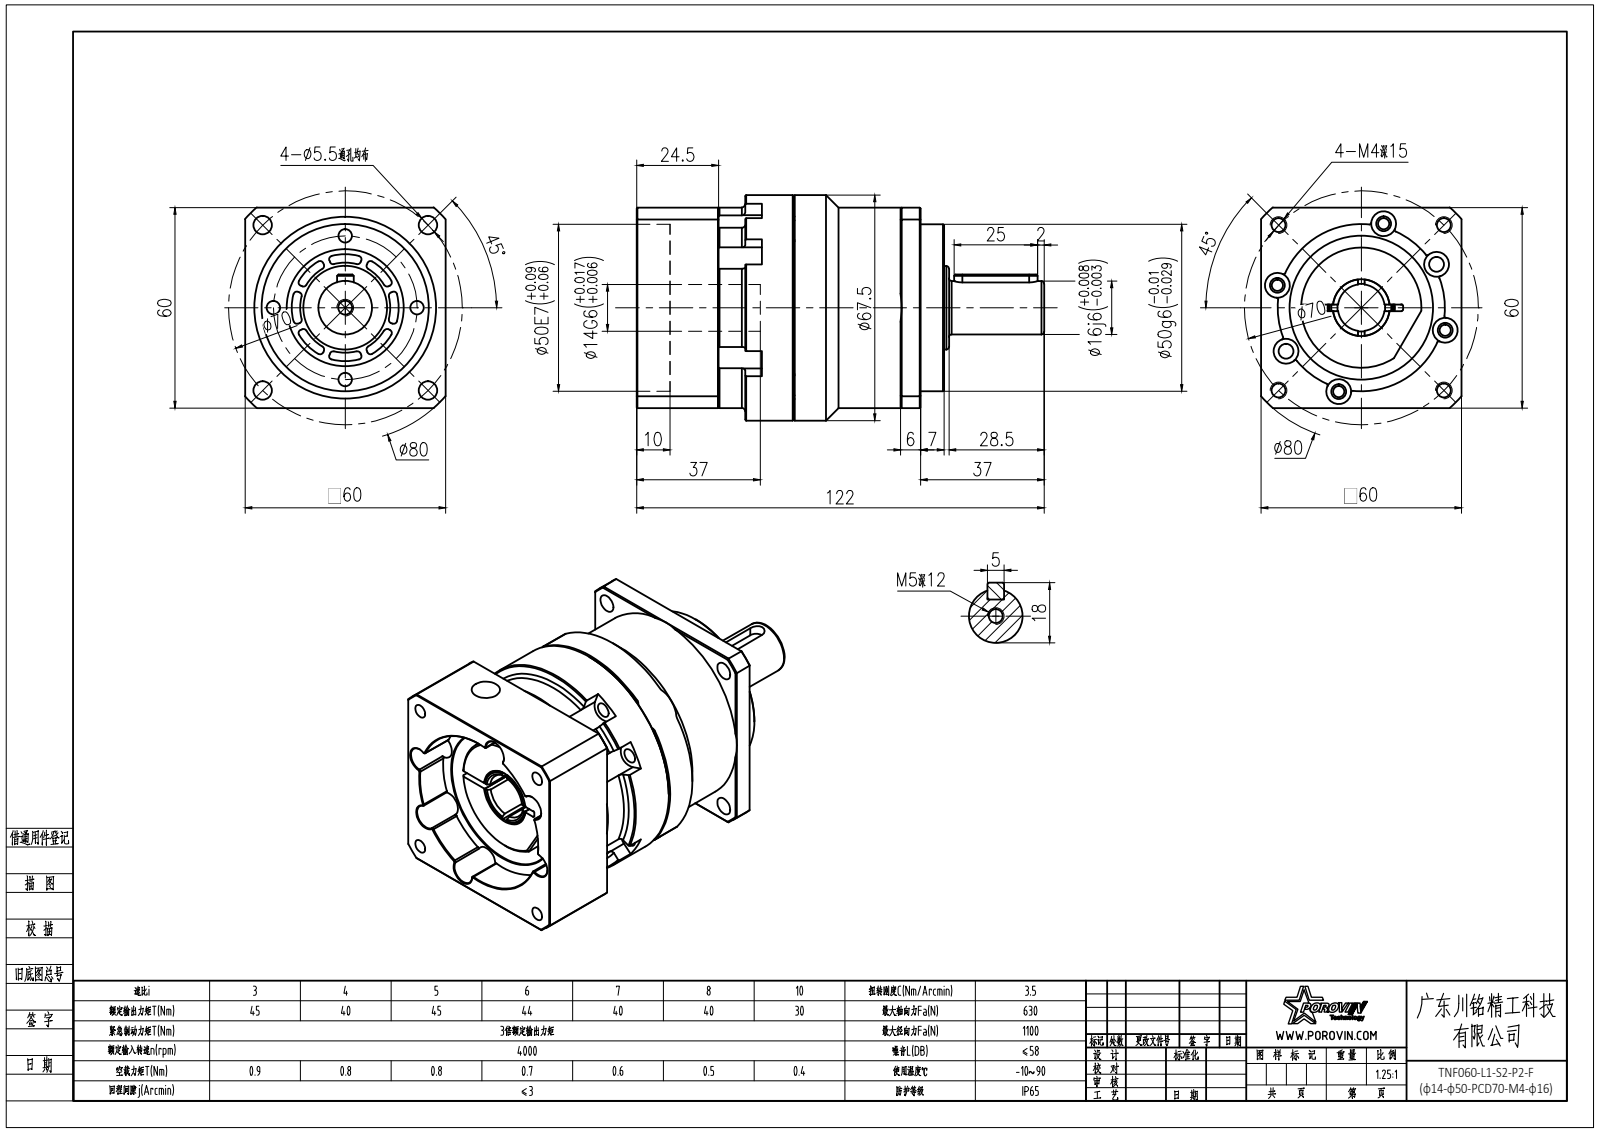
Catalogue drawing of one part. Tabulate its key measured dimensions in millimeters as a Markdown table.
| quantity | value |
| --- | --- |
| part name | hexagon socket head cap screws gb_GB_FASTENER_SCREWS_HSHCS M4X16-N; spring lock washers--normal type gb_GB_FASTENER_WASHER_SW 4; 前齿圈加出轴 KS60外形图; hexagon socket head cap screws gb_GB_FASTENER_SCREWS_HSHCS M4X20-N (+2 more) |
| STEP written by | SolidWorks 2016 (CONFIG_CONTROL_DESIGN) |
| units | millimeters |
| bodies | 32 solids, 1075 faces (407 planar, 396 cylindrical, 272 other) |
| overall size | 122 × 67.5 × 67.5 |
| volume | 237 671 mm³ |
| surface area | 67 766 mm² |
| round holes (diameter × count) | 4.4 × 12, 4.5 × 12, 3.3 × 10, 7.5 × 6, 5.5 × 5, 4 × 4, 4.2 × 2, 5.2 × 1, 8.5 × 1, 14 × 1, 14.2 × 1, 25 × 1 |
| round bosses / shafts (diameter × count) | 7 × 12, 6.6 × 12, 4 × 12, 67.5 × 1, 60 × 1, 36 × 1, 22.5 × 1, 20 × 1 |
| partial cylindrical surfaces (radius × count) | 0.5 × 36, 1 × 32, 3.75 × 6, 2.5 × 2, 4.75 × 1, 13.5 × 1, 16 × 1, 40 × 1 |
| main face-to-face distances | 60, 38, 22.5, 5, 60.5, 11, 27.5, 33, 13, 29 |
| hole center spacings | 24.96, 52.46, 8.62, 26, 30.5, 7.64, 16.02, 18.02 |
